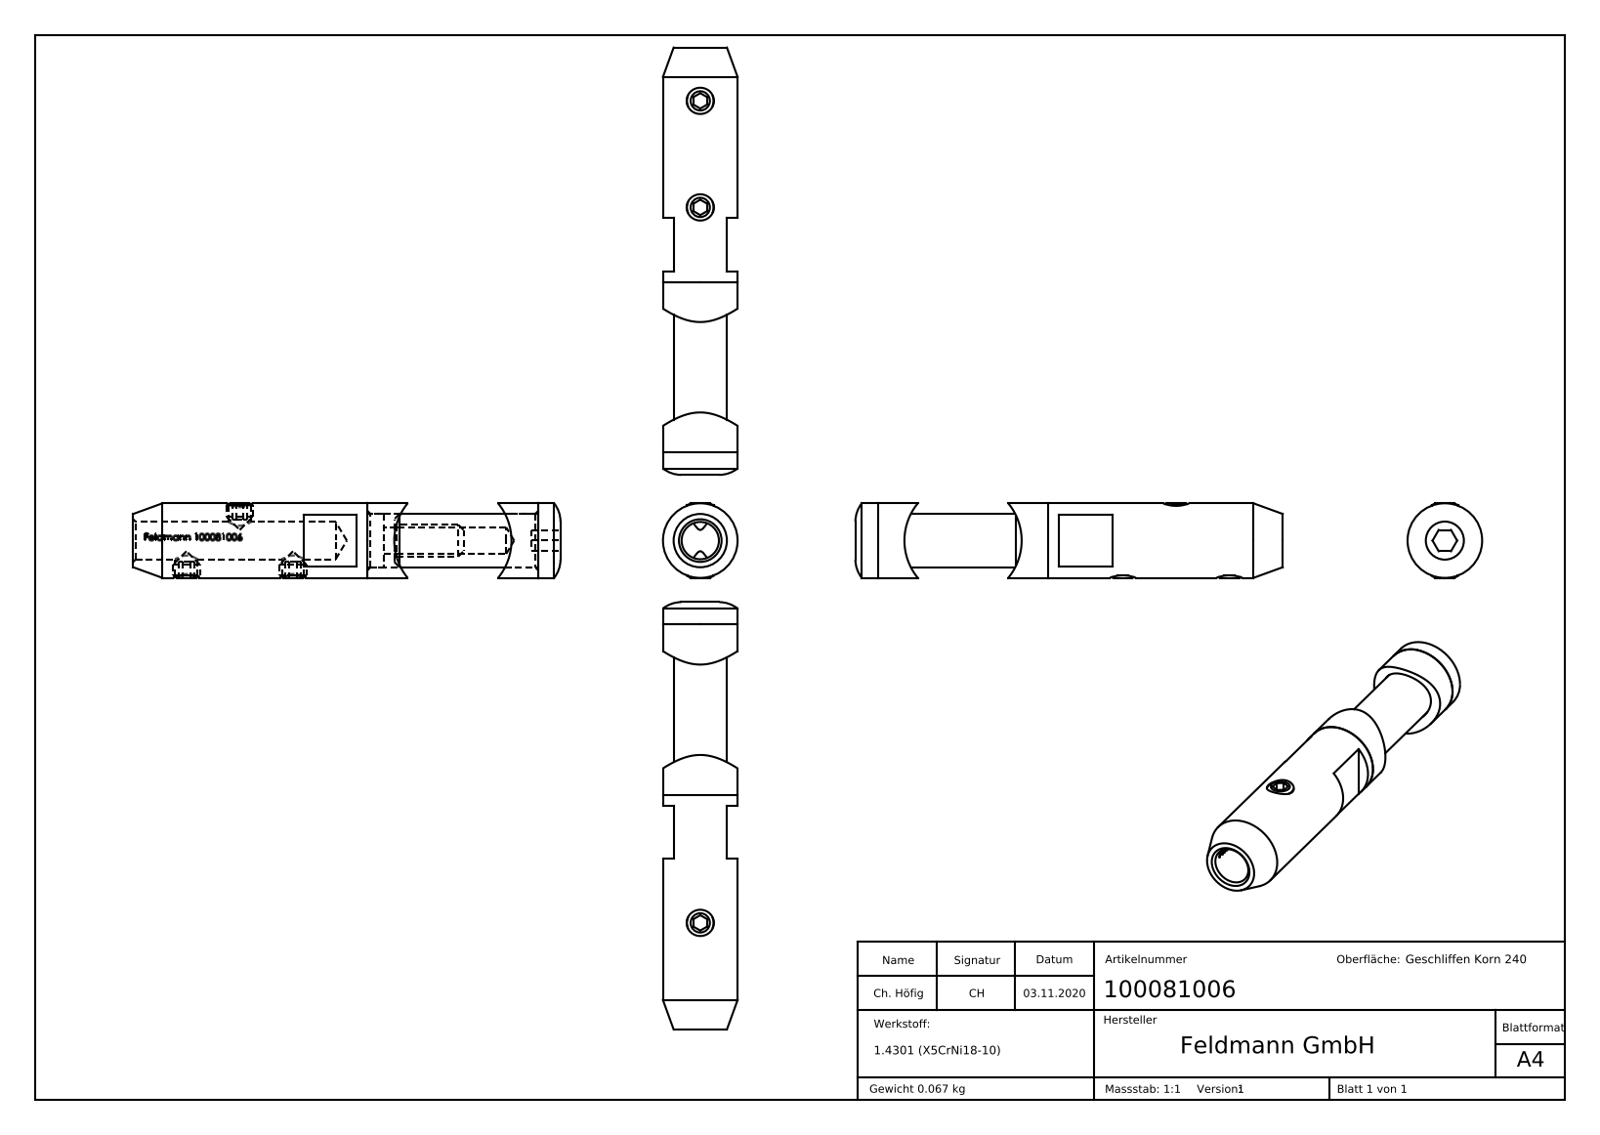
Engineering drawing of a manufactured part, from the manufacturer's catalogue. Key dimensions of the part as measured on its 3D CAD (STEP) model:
Part name (STEP PRODUCT): 10008100X Teil2_10008100X Teil2; 10008100X Teil1; 10008100X Teil1_100081006 Teil1; 100081006 (+5 more)
STEP written by: SolidWorks 2018 (CONFIG_CONTROL_DESIGN)
Units: millimetres
Bodies: 7 solids, 345 faces (116 planar, 72 cylindrical, 157 other)
Overall size (bounding box): 80.2 × 14 × 14
Volume: 8 476 mm³ · Surface area: 6 651 mm²
Round holes (diameter × count): ⌀4.2 ×3, ⌀5 ×1, ⌀7 ×1, ⌀10.1 ×1
Round bosses / shafts (diameter × count): ⌀5 ×3, ⌀14 ×1, ⌀10 ×1, ⌀6 ×1
Partial cylindrical surfaces — rounded edges, fillets, slot ends (radius × count): R3.6 ×1, R11 ×1
Main face-to-face distances: 32, 10, 3, 2, 5, 29, 44, 2.5, 15, 4
Hole centre spacings: 10, 20
